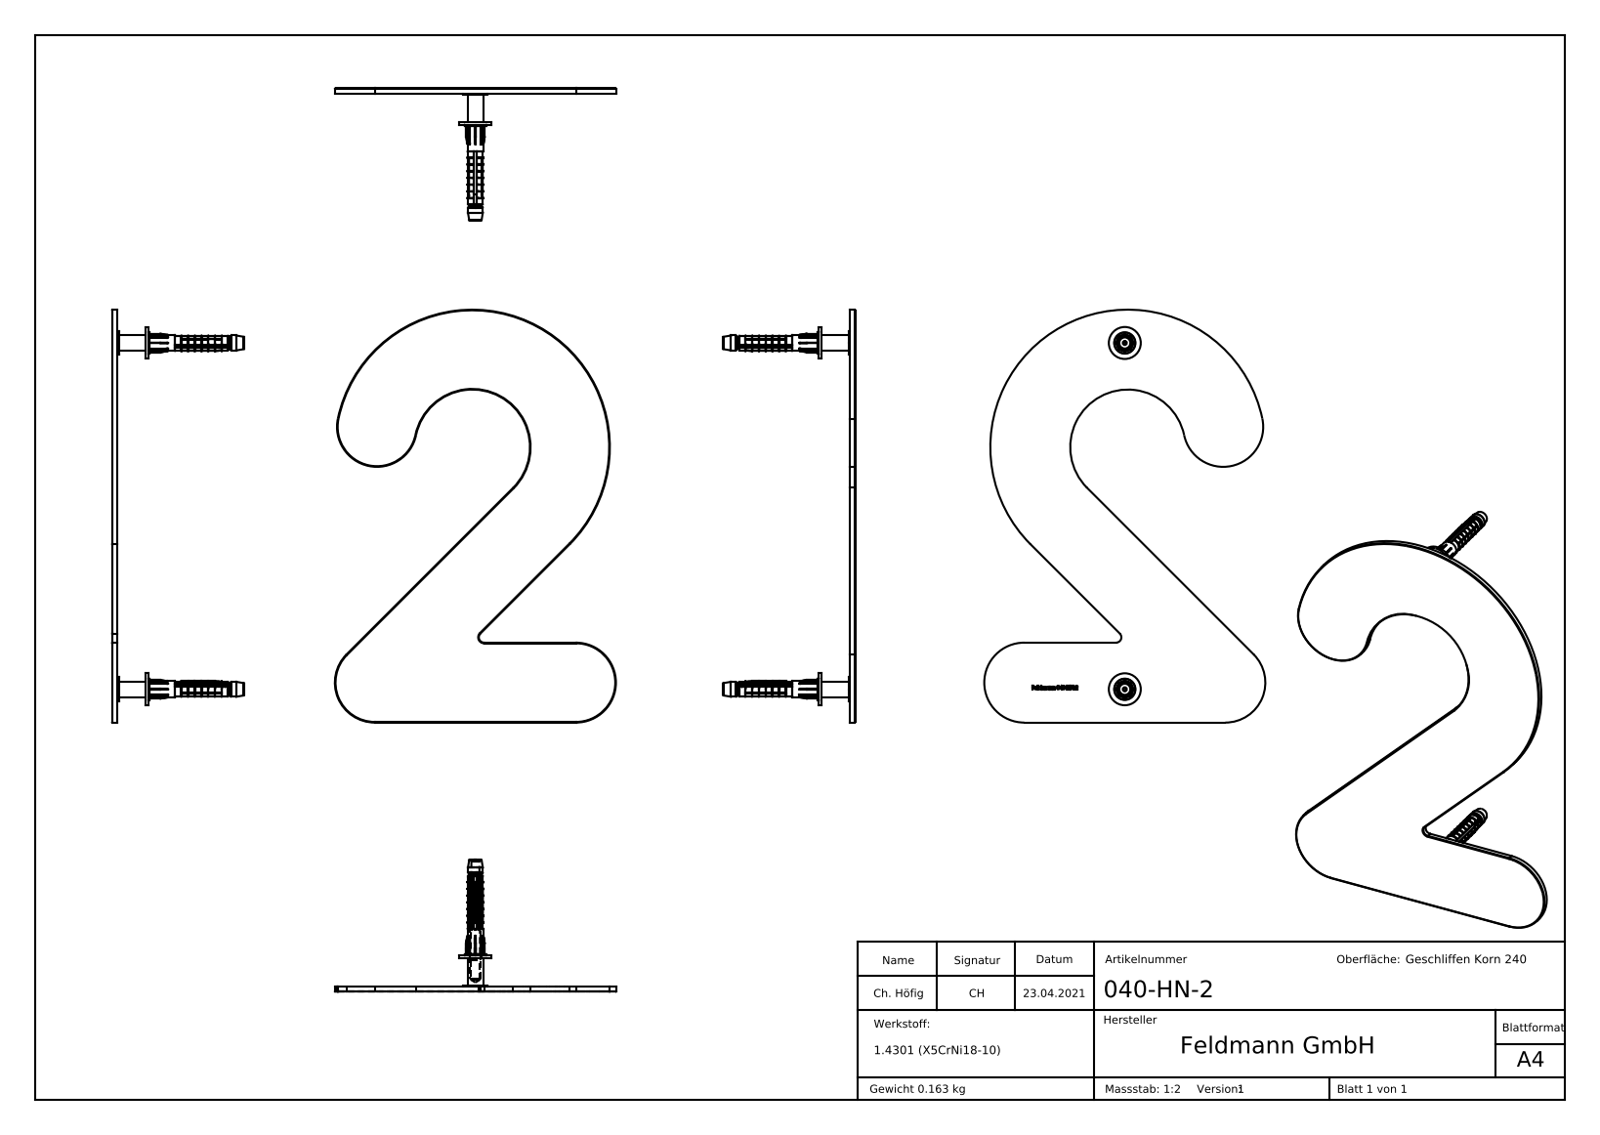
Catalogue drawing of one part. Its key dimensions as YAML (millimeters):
part_name: "040-HN-X Teil1_040-HN-2 Teil1; 040-HN-2; 040-HN-X Teil2_040-HN-X Teil2; 040-HN-X Teil2 (+5 more)"
step_written_by: "SolidWorks 2018 (CONFIG_CONTROL_DESIGN)"
units: millimeters
bodies: {solids: 7, faces: 1559, planar: 361, cylindrical: 391, other: 807}
overall_size: [10000, 5217.43, 4607.88]
volume: 21544
surface_area: 24514
round_holes:
  - {diameter: 3.3, count: 2}
  - {diameter: 4.3, count: 2}
round_bosses_or_shafts:
  - {diameter: 12, count: 2}
  - {diameter: 9, count: 2}
  - {diameter: 8, count: 2}
  - {diameter: 6, count: 2}
  - {diameter: 5.8, count: 2}
  - {diameter: 5.6, count: 2}
  - {diameter: 4.6, count: 2}
  - {diameter: 4, count: 2}
partial_cylinders:
  - {radius: 0.1, count: 22}
  - {radius: 0.25, count: 4}
  - {radius: 15, count: 3}
  - {radius: 3.5, count: 2}
  - {radius: 2, count: 1}
  - {radius: 21.61, count: 1}
  - {radius: 51.61, count: 1}
face_to_face_distances: [2, 11.6, 13.6, 12.5, 1.1, 10.5, 0.5, 2.5, 29.99, 10]
hole_center_spacings: [130]
